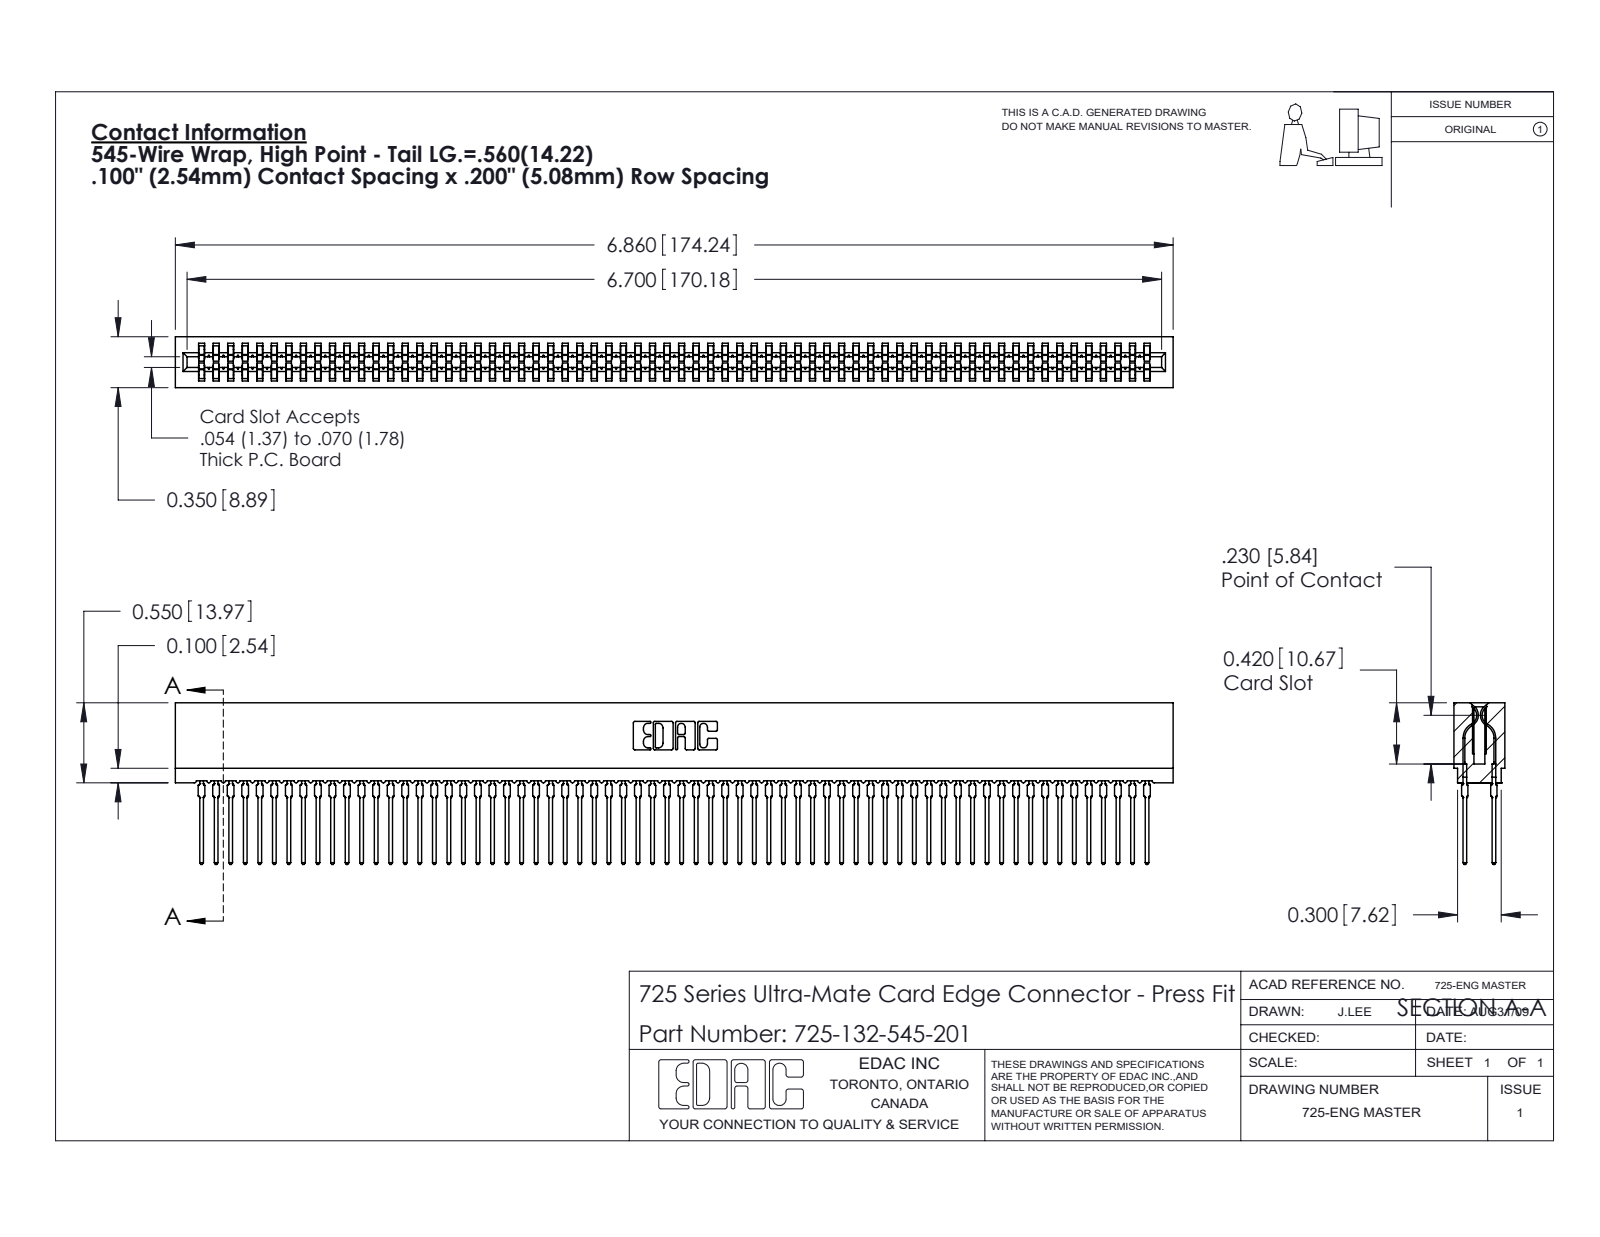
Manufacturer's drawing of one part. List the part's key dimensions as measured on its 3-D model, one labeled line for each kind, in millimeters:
Part name (STEP PRODUCT): 725-132-545-201; 725 Part_Insulator Option - 01; 745-292-001_545
STEP written by: SolidWorks 2020 (CONFIG_CONTROL_DESIGN)
Units: millimetres
Bodies: 133 solids, 11909 faces (6127 planar, 2350 cylindrical, 3432 other)
Overall size (bounding box): 174.2 × 28.2 × 8.9
Volume: 14 200 mm³ · Surface area: 32 440 mm²
Partial cylindrical surfaces — rounded edges, fillets, slot ends (radius × count): R0.5 ×264, R0.4 ×132, R0.3 ×22, R0.1 ×8, R0.3 ×8, R0.2 ×6, R0.8 ×6, R0.7 ×3
Main face-to-face distances: 1.6, 7.3, 5.1, 8.9, 5.4, 3.5, 1.9, 3.8, 2.2, 6.7
